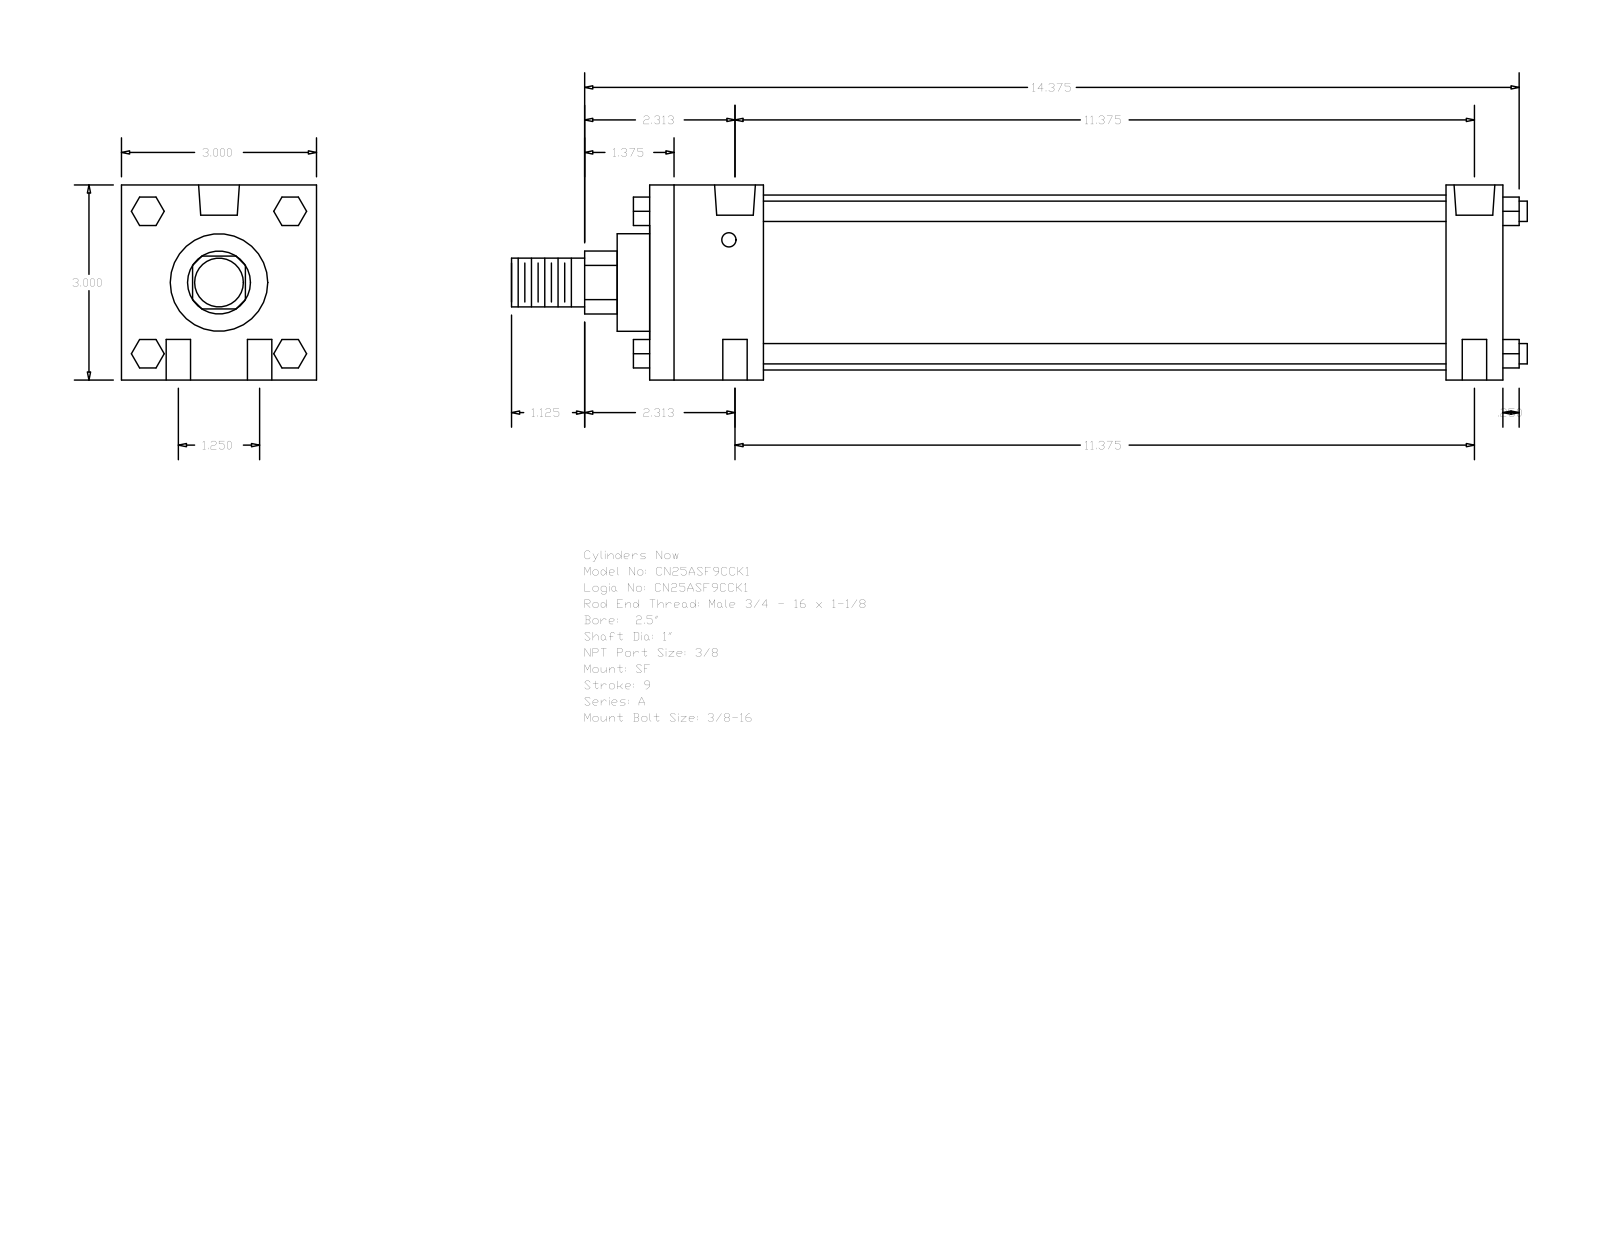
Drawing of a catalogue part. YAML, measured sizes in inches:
part_name: "A_SF__0250_1"
step_written_by: "GSSL Pune (CONFIG_CONTROL_DESIGN)"
units: inches
bodies: {solids: 0, faces: 124, planar: 94, cylindrical: 30, other: 0}
overall_size: [15.625, 3, 3]
round_holes:
  - {diameter: 0.375, count: 4}
  - {diameter: 0.219, count: 2}
  - {diameter: 0.627, count: 2}
round_bosses_or_shafts:
  - {diameter: 0.313, count: 4}
  - {diameter: 2.69, count: 1}
  - {diameter: 1.5, count: 1}
  - {diameter: 1, count: 1}
  - {diameter: 0.75, count: 1}
partial_cylinders:
  - {radius: 0.484, count: 1}
face_to_face_distances: [3, 13.125, 12.25, 0.875, 1.75, 10.5, 11.375, 0.5, 13.625, 0.25]
hole_center_spacings: [0.625, 11.392, 11.375, 1.25, 11.443, 11.562]
